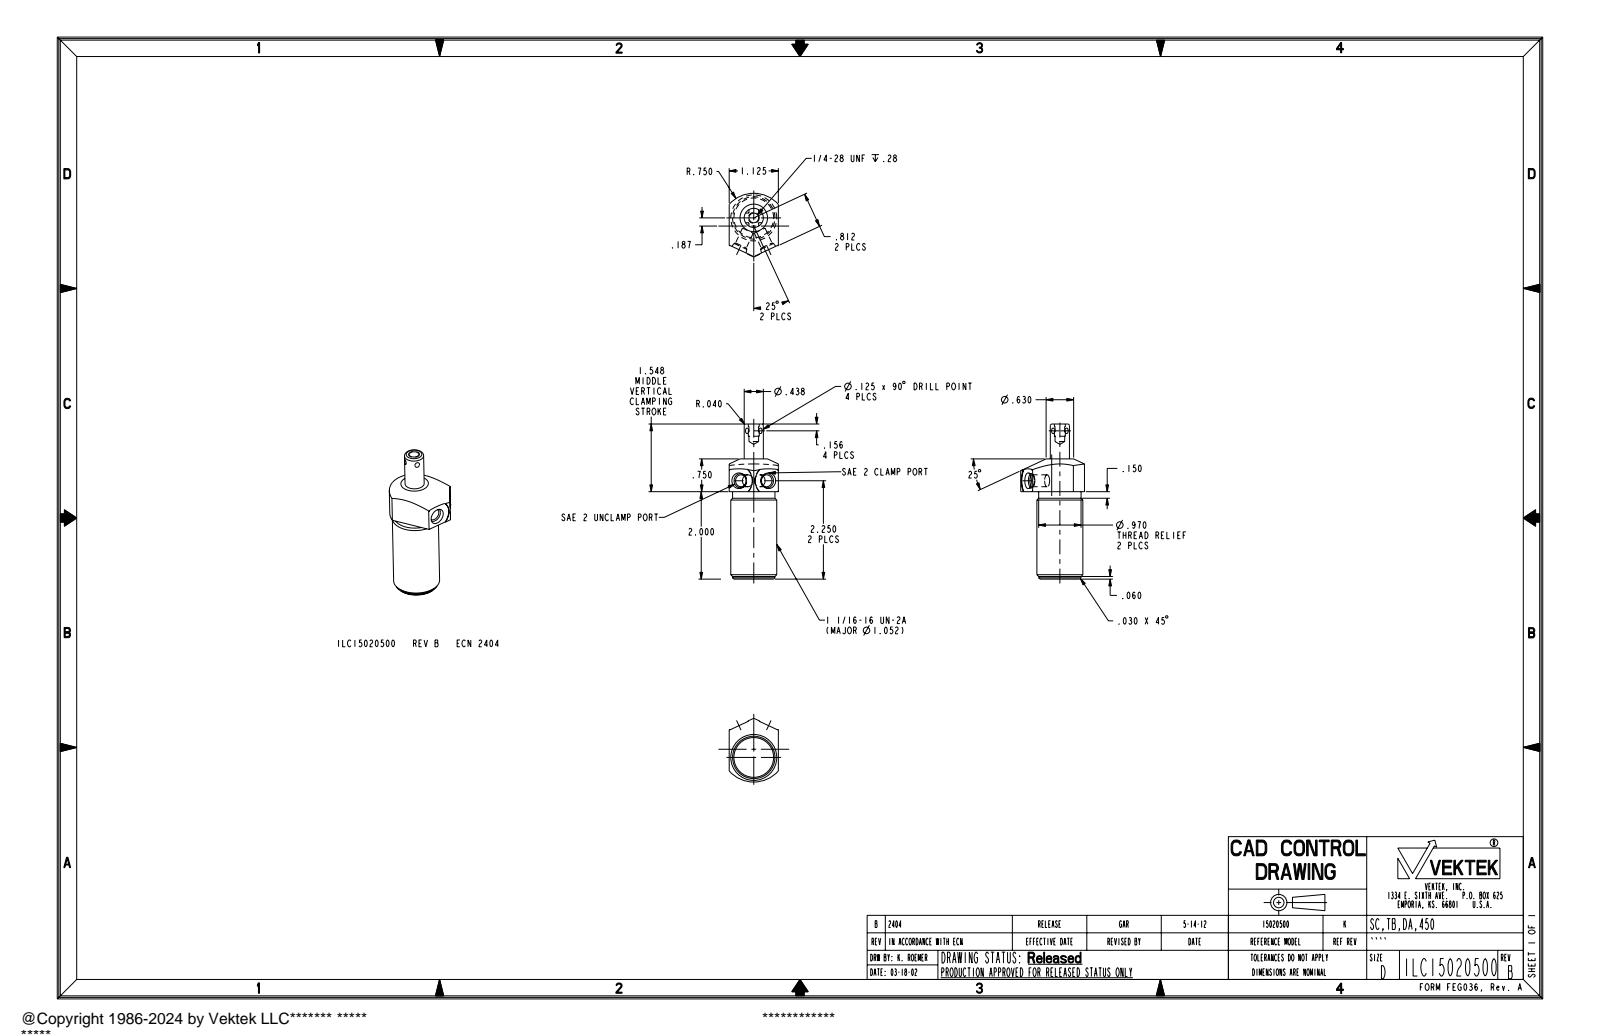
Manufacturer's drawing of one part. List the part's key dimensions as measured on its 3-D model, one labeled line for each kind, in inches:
Part name (STEP PRODUCT): ILC15020500
STEP written by: PRO/ENGINEER BY PARAMETRIC TECHNOLOGY CORPORATION, 2007460 (AUTOMOTIVE_DESIGN_CC2)
Units: inches
Bodies: 1 solid, 68 faces (17 planar, 23 cylindrical, 28 other)
Overall size (bounding box): 3.548 × 1.459 × 1.125
Volume: 2.681 in³ · Surface area: 14.47 in²
Round holes (diameter × count): ⌀0.272 ×2, ⌀0.221 ×1
Round bosses / shafts (diameter × count): ⌀1.052 ×1, ⌀0.97 ×1, ⌀0.438 ×1, ⌀0.25 ×1
Partial cylindrical surfaces — rounded edges, fillets, slot ends (radius × count): R0.341 ×2, R0.75 ×1
Main face-to-face distances: 2, 1.125, 2.75, 0.75, 0.48, 3.548, 1.548, 0.798, 0.49, 0.49
